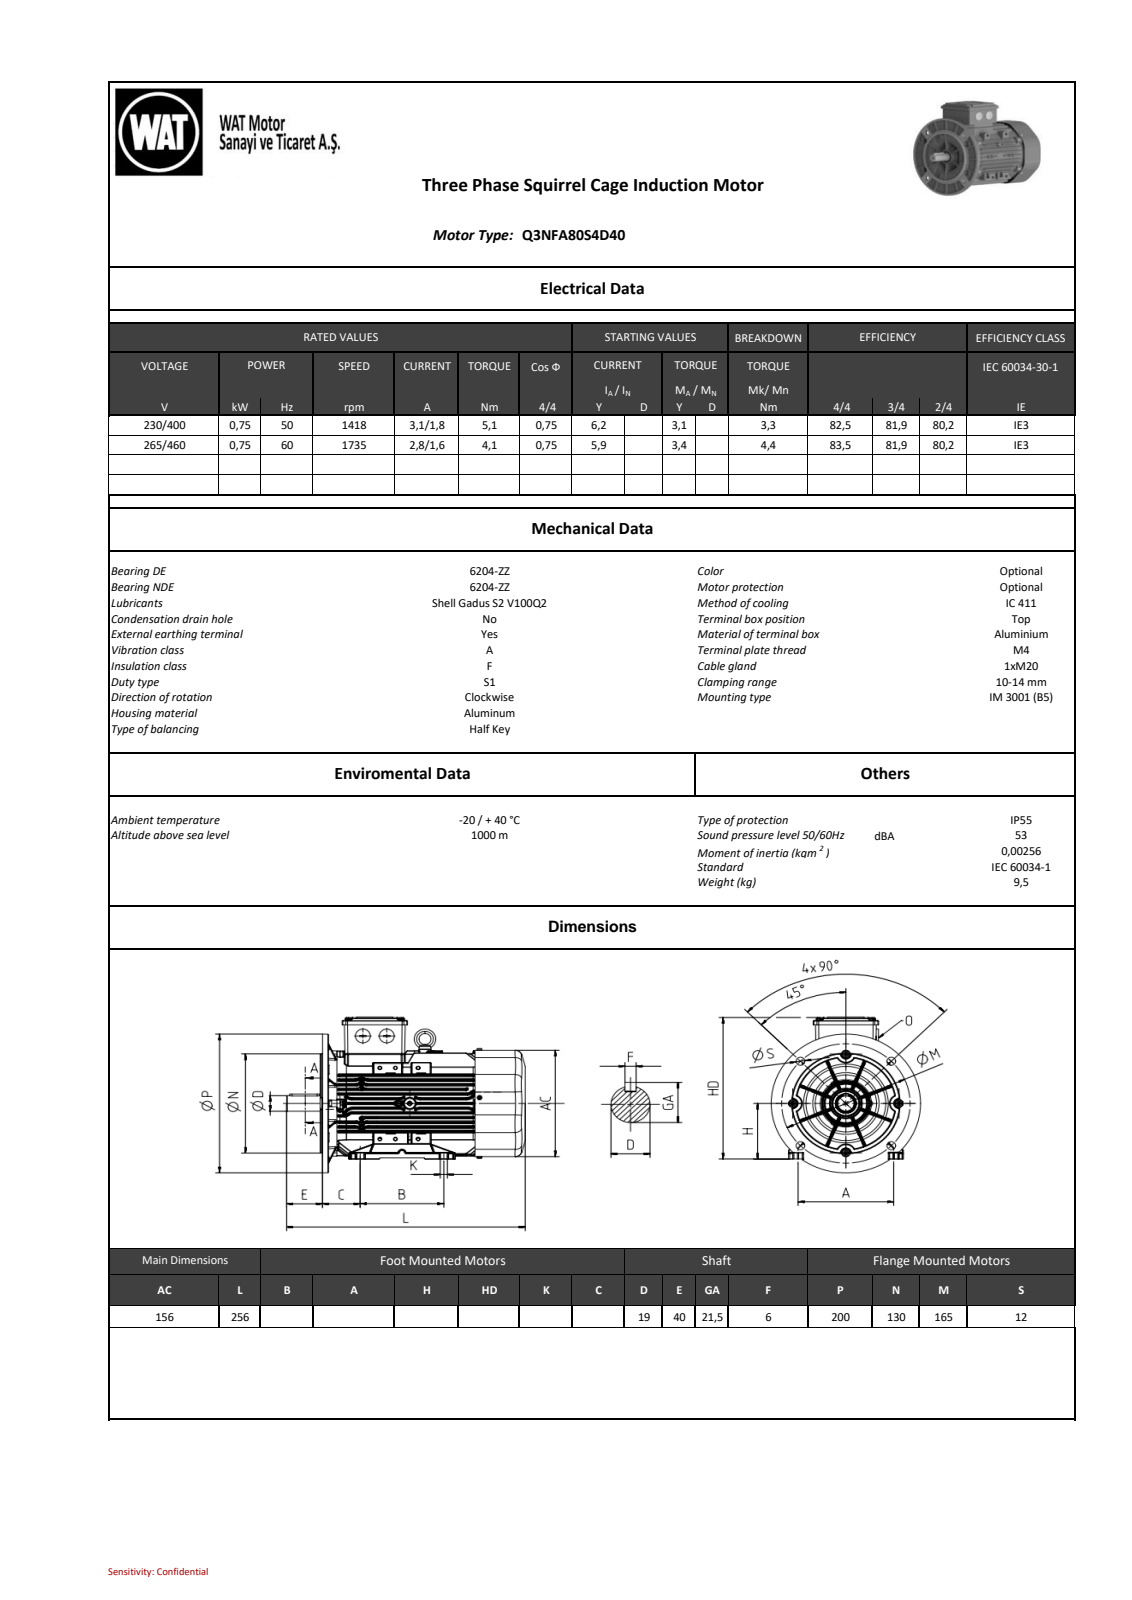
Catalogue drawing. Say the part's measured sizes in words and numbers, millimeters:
The part is named "260320808B12ligj". Its 3-D file was written by "SIEMENS PLM Software NX 11.0 (AUTOMOTIVE_DESIGN)". It is 0 solids with 5215 faces: 1229 planar, 2034 cylindrical and 1952 other. Overall it measures 255.71 by 205.95 by 198 millimeters. Round holes: 1 of diameter 4, 1 of diameter 4.5, 1 of diameter 6.4, 1 of diameter 13, 1 of diameter 27.8, 1 of diameter 28. Round bosses or shafts: 7 of diameter 8, 3 of diameter 5, 2 of diameter 20, 1 of diameter 134.4, 1 of diameter 130, 1 of diameter 29.5, 1 of diameter 19, 1 of diameter 18.4. Partial cylindrical surfaces (rounded edges, fillets, slot ends): 545 of radius 0.5, 448 of radius 1, 159 of radius 0.8, 103 of radius 0.4, 45 of radius 0.25, 20 of radius 3, 19 of radius 4, 18 of radius 0.2. The main face-to-face distances are 6, 0.8, 209.71, 215.71, 30, 36.21, 173.5, 179.5, 3, 206.71. The hole center spacings are 106.22.
